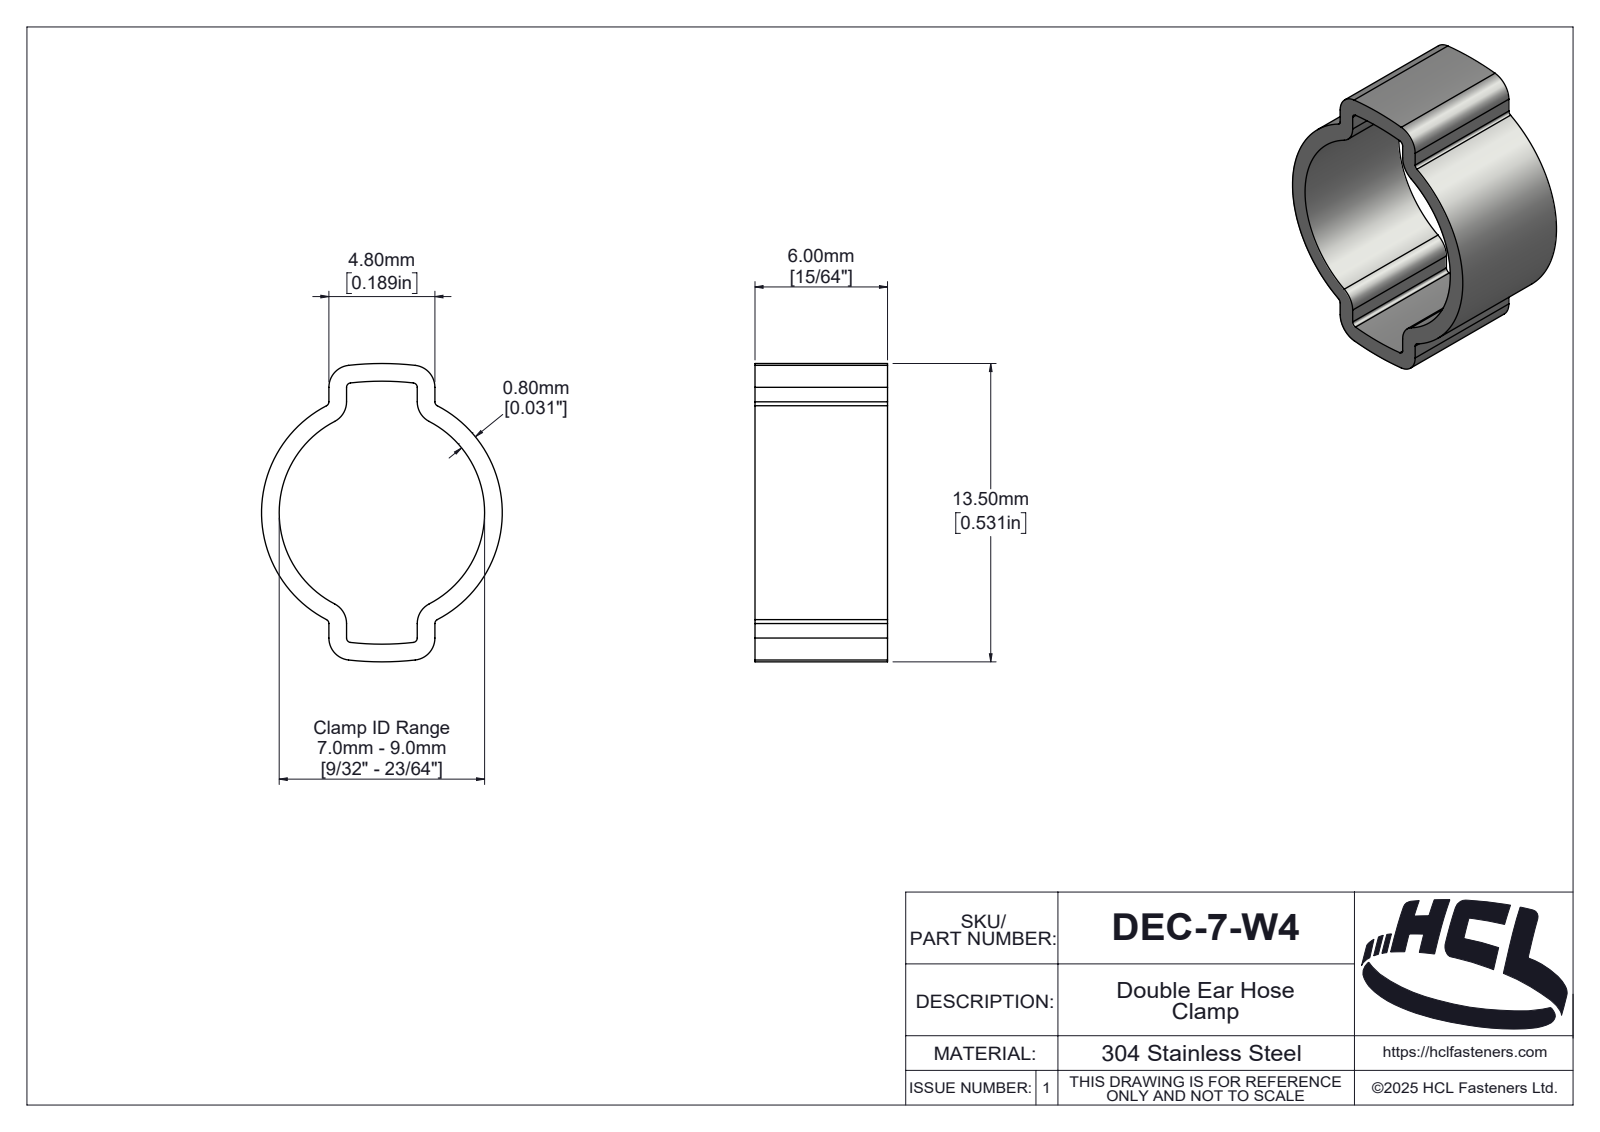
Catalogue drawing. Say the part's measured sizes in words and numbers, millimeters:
The part is named "DEC-7-W4". Its 3-D file was written by "SolidWorks 2025 (AUTOMOTIVE_DESIGN)". It is 1 solid with 137 faces: 12 planar, 76 cylindrical and 49 other. Overall it measures 13.5 by 10.9 by 6 millimeters. Its volume is 176 cubic millimeters and its surface area 502 square millimeters. Partial cylindrical surfaces (rounded edges, fillets, slot ends): 8 of radius 0.2, 8 of radius 1, 2 of radius 12.85, 2 of radius 13.65, 1 of radius 0.13, 1 of radius 0.54, 1 of radius 0.67, 1 of radius 0.71. The main face-to-face distances are 6, 0.8, 4, 4.8, 3.2, 2.22, 1.42, 1.78, 2.58, 2.32.
